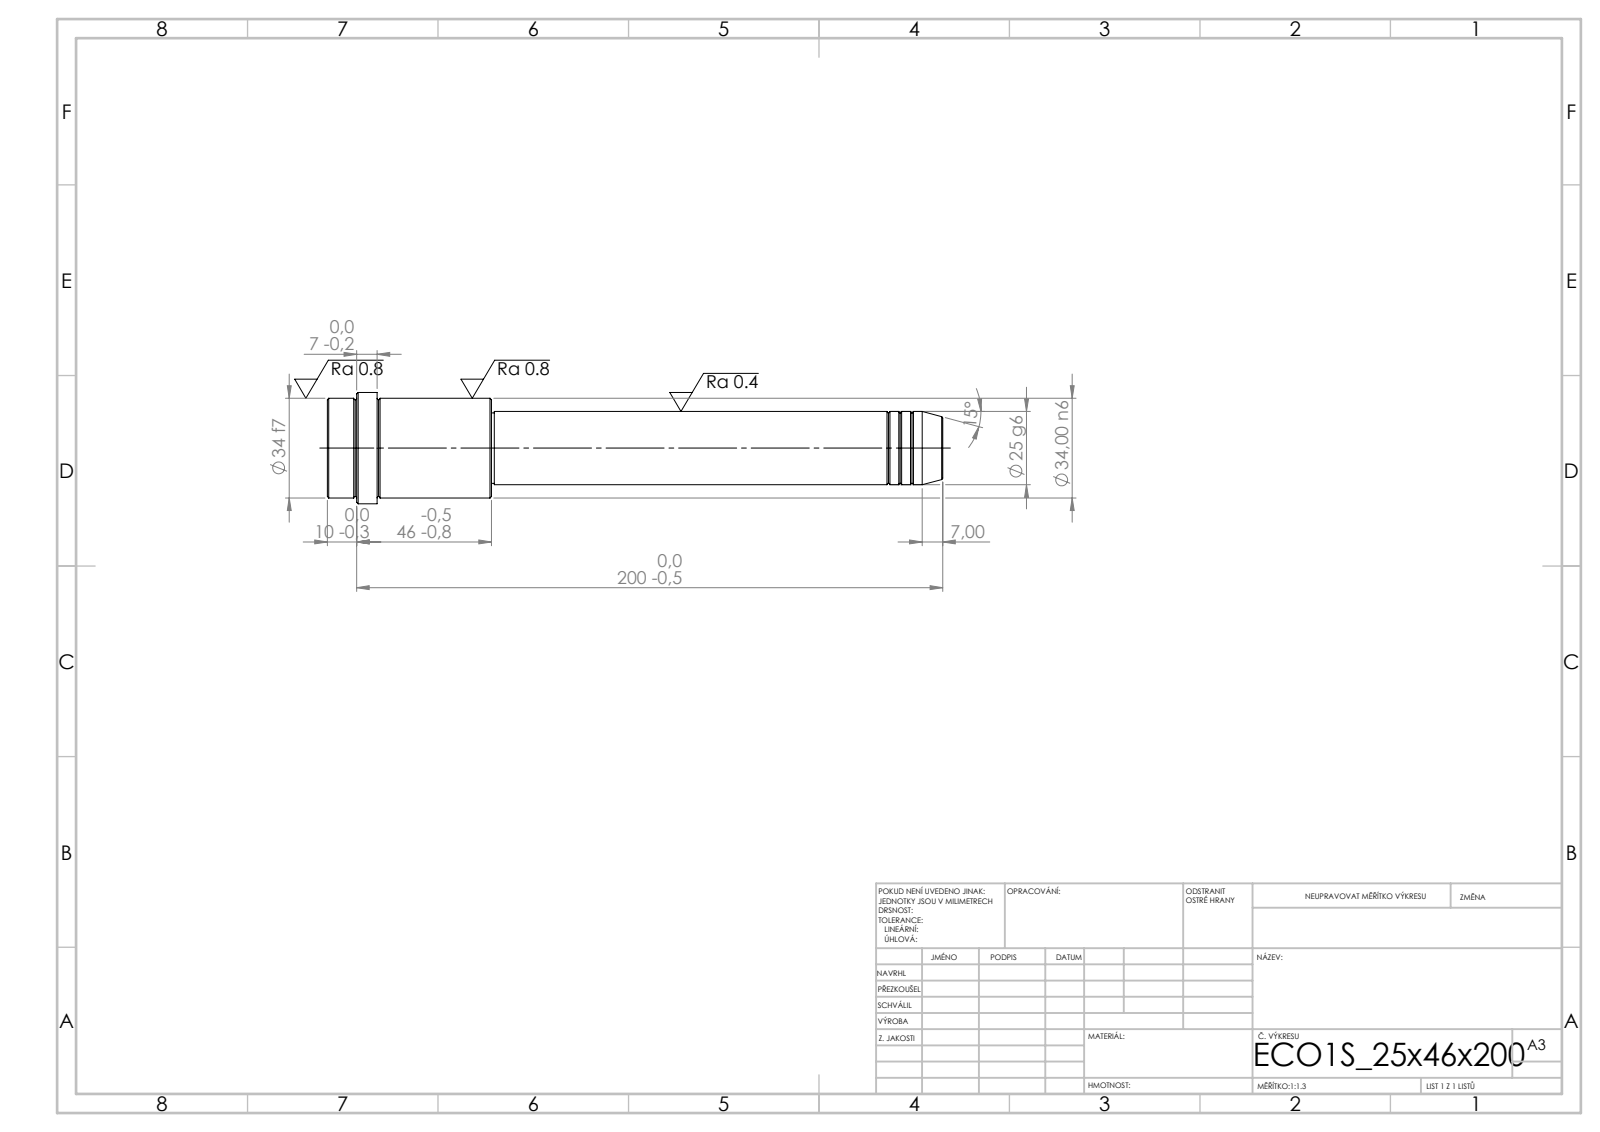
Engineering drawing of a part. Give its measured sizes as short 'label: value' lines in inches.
written by: SolidWorks 2019 (CONFIG_CONTROL_DESIGN)
unit: in
bodies: 1 solid, 52 faces (6 planar, 16 cylindrical, 30 other)
size: 8.268 × 1.496 × 1.496
volume: 7.767 in³; area: 31.75 in²
bosses: 1× ⌀1.496, 1× ⌀1.339, 1× ⌀0.984, 1× ⌀0.945
face distances: 2.205, 6.063, 8.268, 7.598, 1.535, 0.669, 7.874, 1.811, 0.276, 0.394
